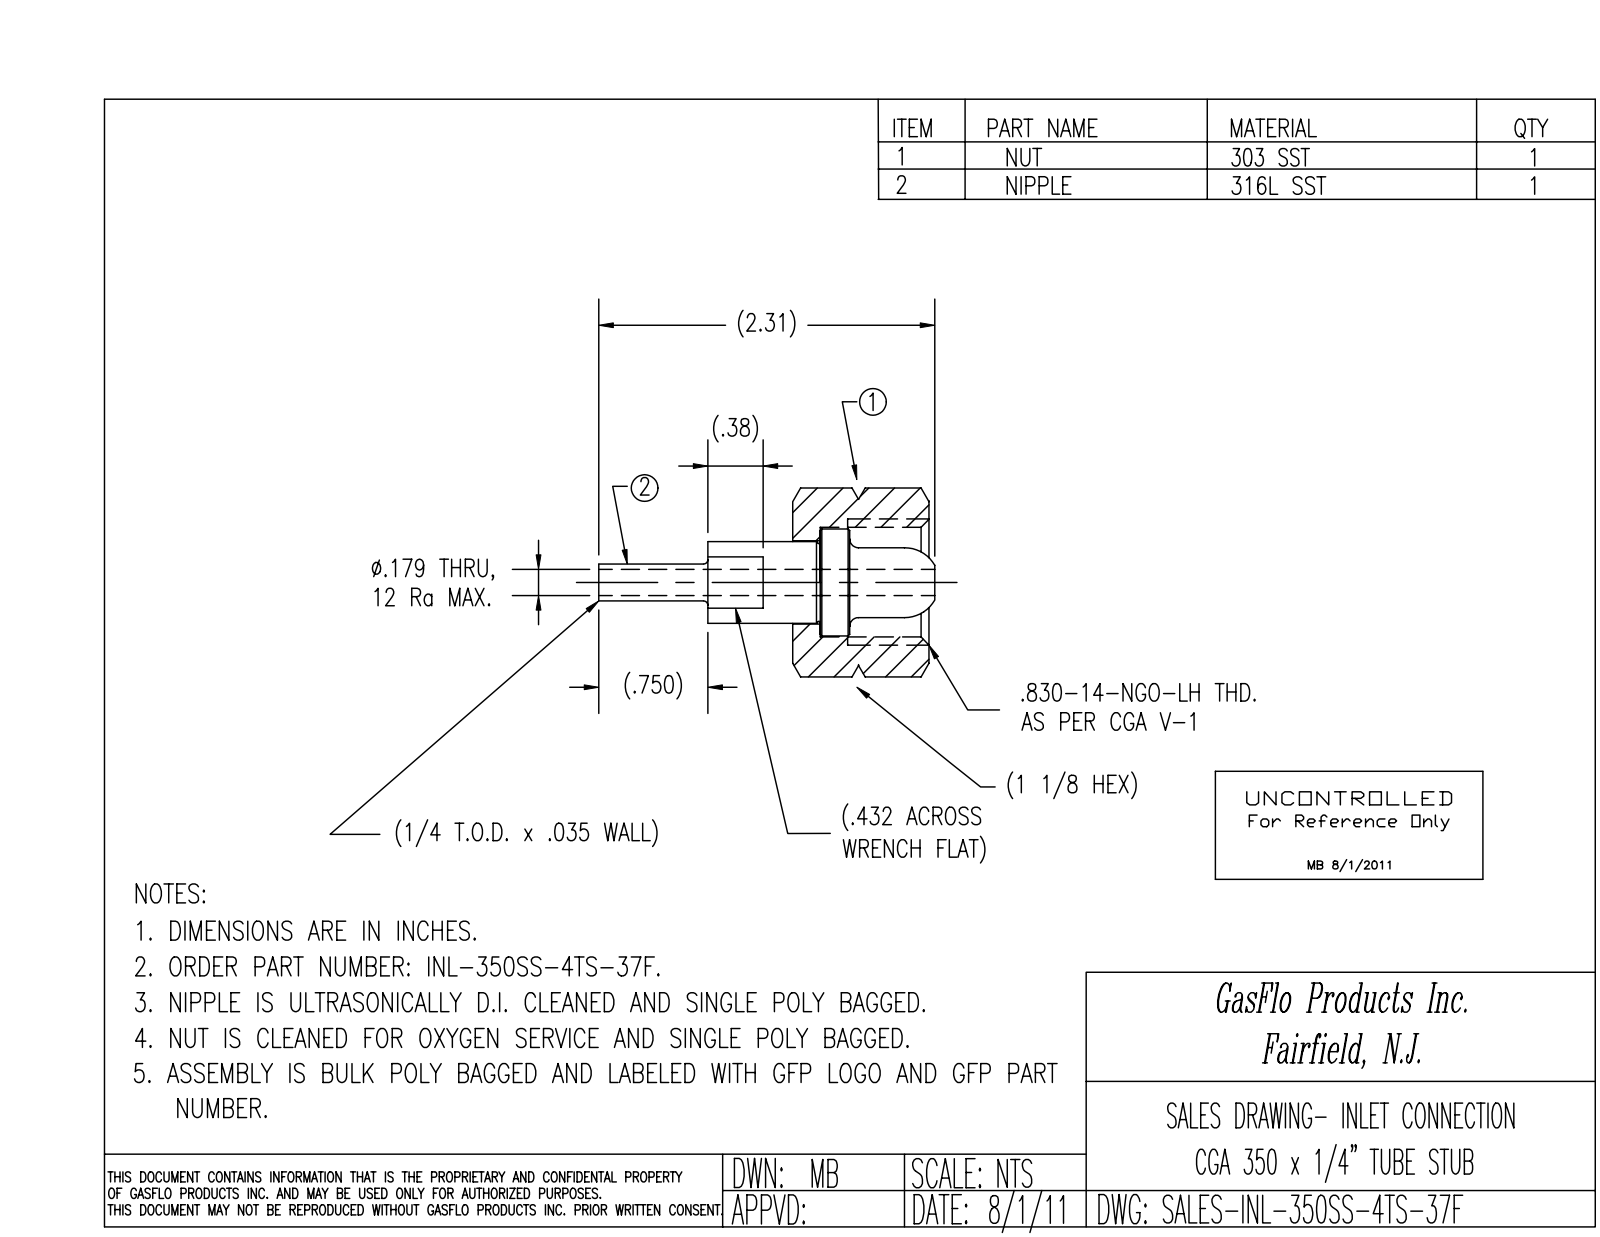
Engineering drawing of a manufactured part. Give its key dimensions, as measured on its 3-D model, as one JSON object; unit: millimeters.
{"part_name": "INL-350SS-4TS-37F", "step_written_by": "SolidWorks 2018 (CONFIG_CONTROL_DESIGN)", "units": "millimeters", "bodies": {"solids": 1, "faces": 140, "planar": 35, "cylindrical": 10, "other": 95}, "overall_size": [59.4, 33, 28.6], "volume_mm3": 16000, "surface_area_mm2": 7335, "round_holes": [[4.5, 1], [19.2, 1]], "round_bosses_or_shafts": [[14.2, 1], [12.1, 1], [6.4, 1]], "face_to_face_distances": [28.6, 28.6, 24, 16.3, 40.3, 19.8, 8.8, 19.8, 11, 8.8]}
